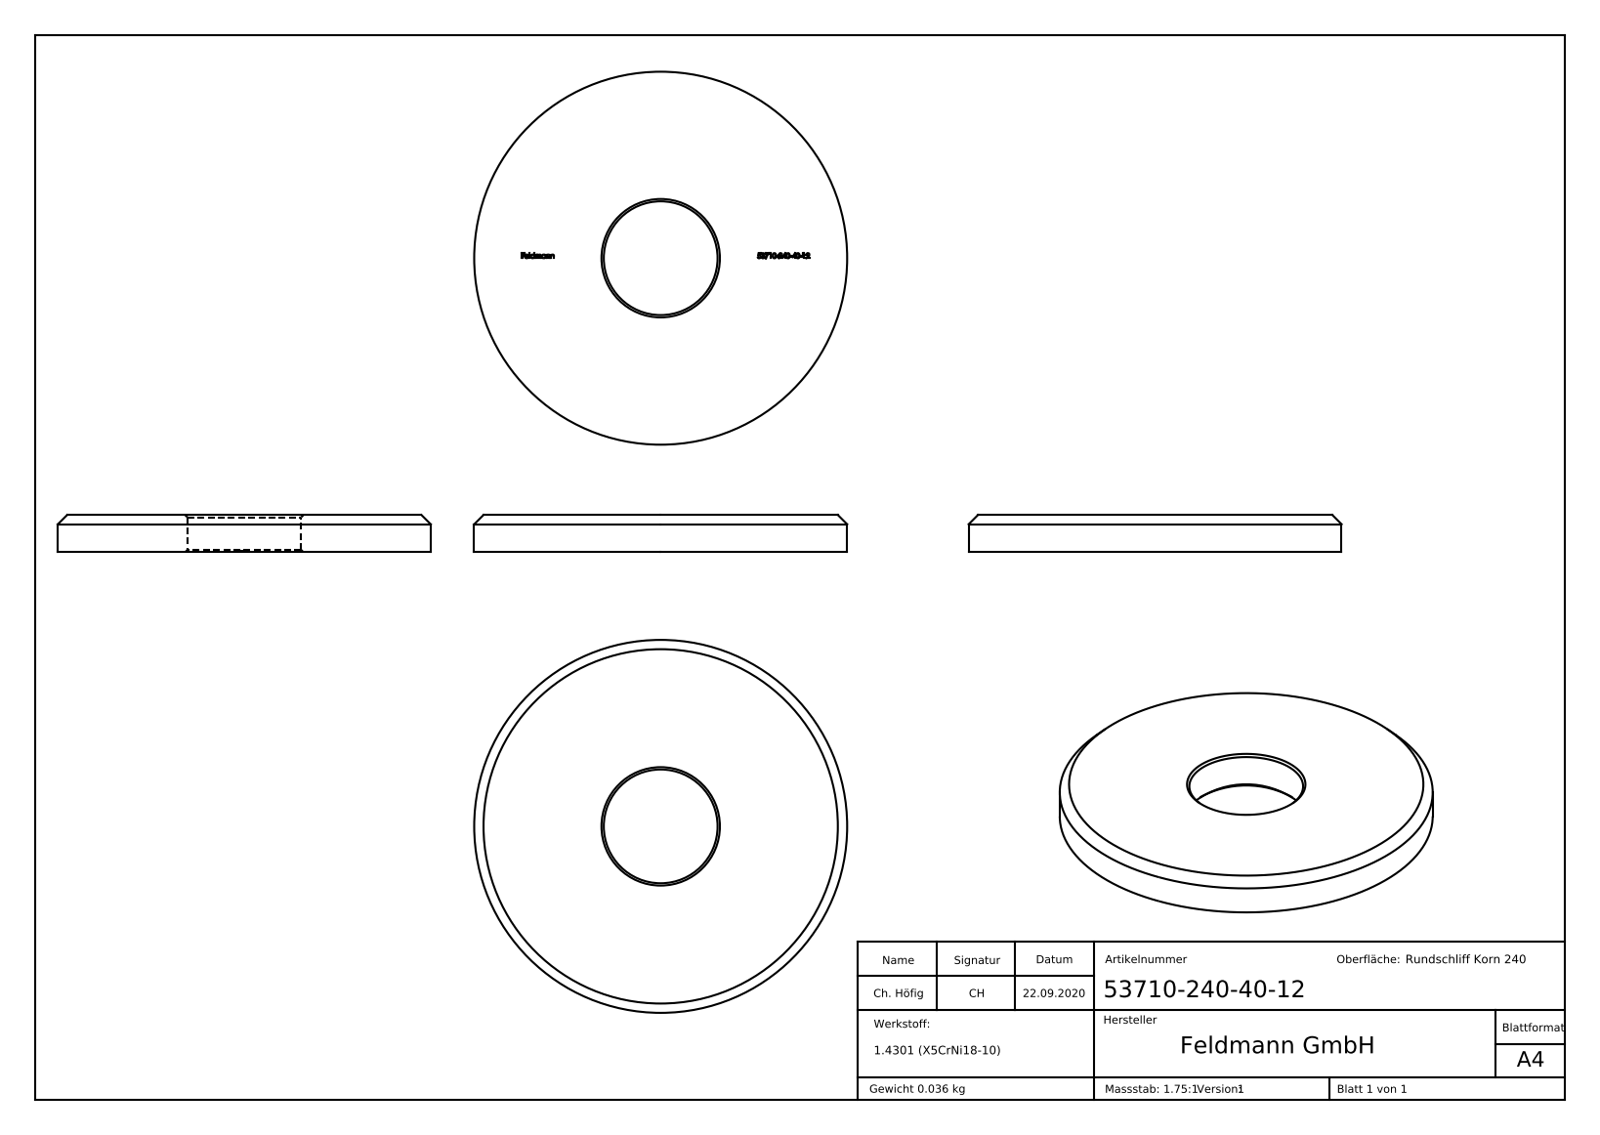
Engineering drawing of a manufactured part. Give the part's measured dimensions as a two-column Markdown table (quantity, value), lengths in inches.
| quantity | value |
| --- | --- |
| part name | 53710-240-40-12 |
| STEP written by | SolidWorks 2018 (CONFIG_CONTROL_DESIGN) |
| units | inches |
| bodies | 1 solid, 283 faces (164 planar, 4 cylindrical, 115 other) |
| overall size | 1.575 × 1.575 × 0.157 |
| volume | 0.274 in³ |
| surface area | 4.424 in² |
| round holes (diameter × count) | 0.48 × 1 |
| round bosses / shafts (diameter × count) | 1.575 × 1 |
| main face-to-face distances | 0.157, 0.154, 0.014, 0.021, 0.022, 1.018, 1.159, 0.141, 0.032, 1.05 |
